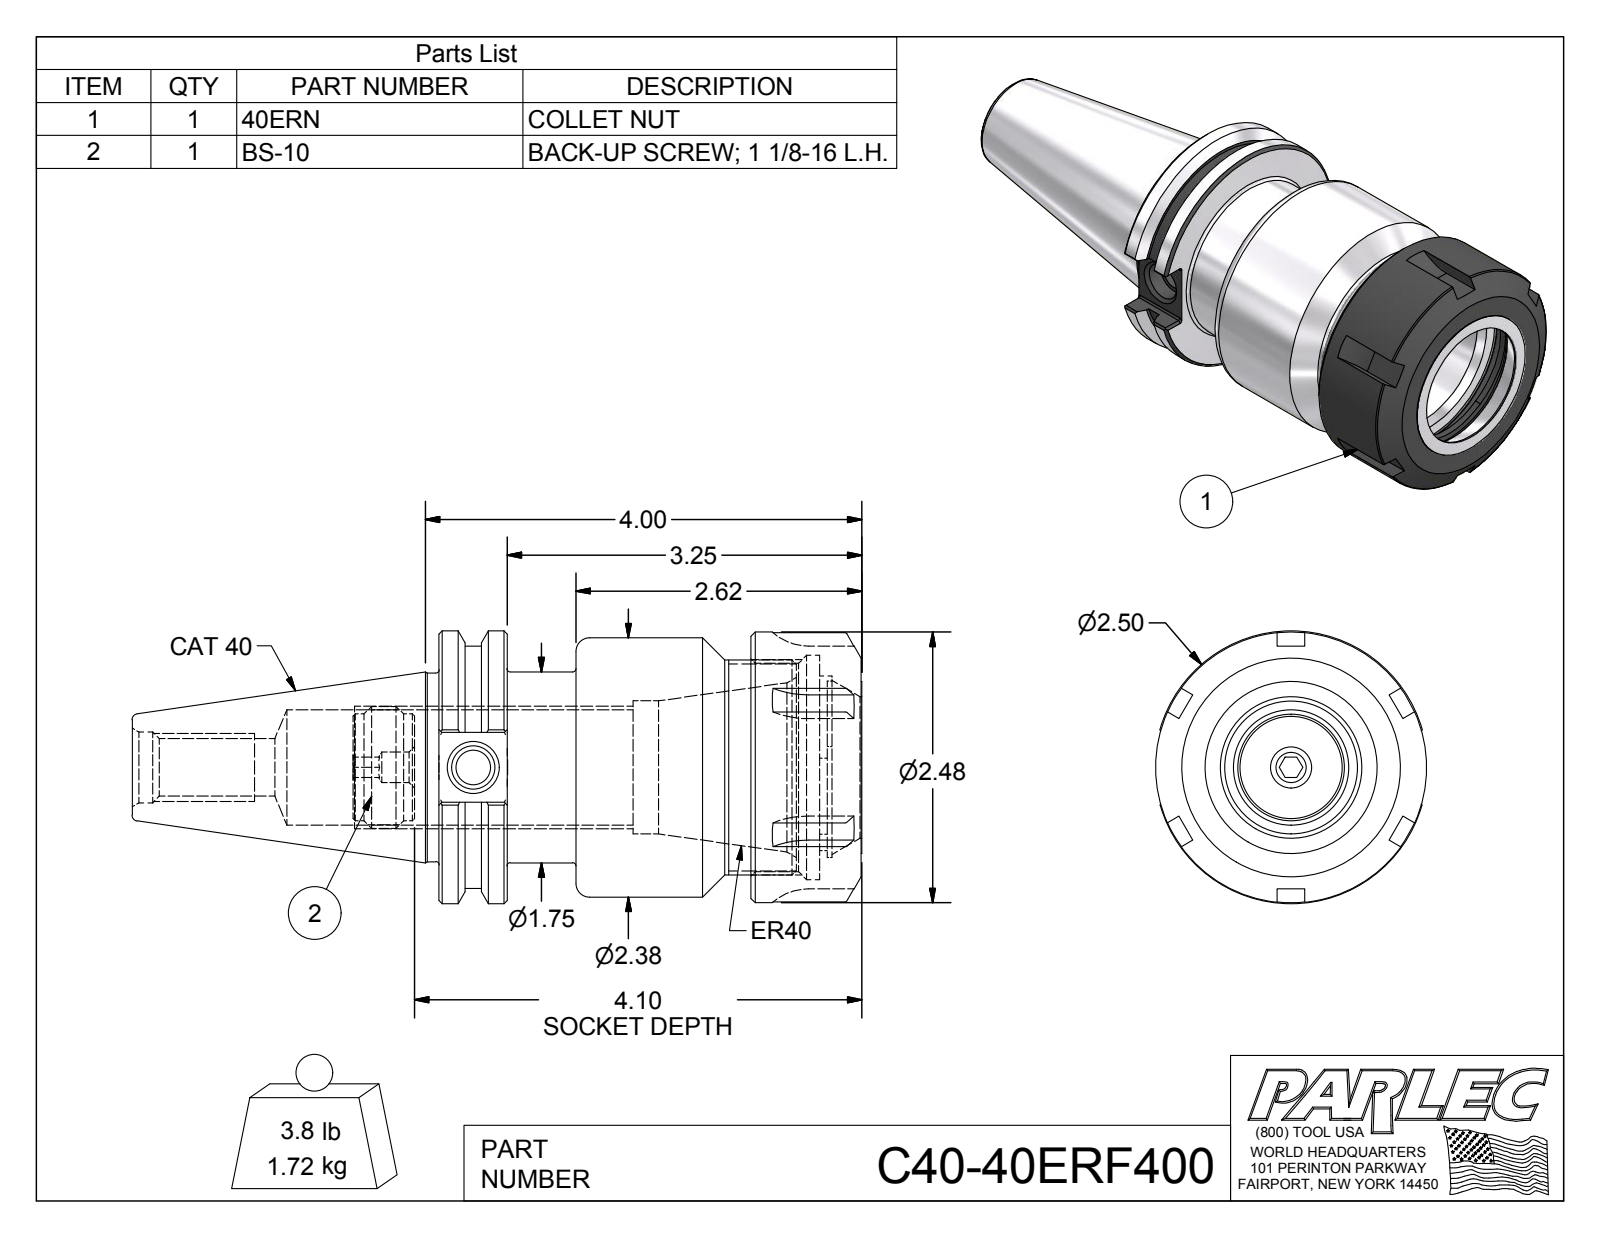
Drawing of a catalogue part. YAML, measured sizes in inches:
part_name: "C40-40ER4-1; 40ERN; BS-10; C40-40ERF400"
step_written_by: "Autodesk Inventor 2016 (AUTOMOTIVE_DESIGN)"
units: inches
bodies: {solids: 3, faces: 188, planar: 76, cylindrical: 52, other: 60}
overall_size: [6.687, 2.5, 2.48]
volume: 13.56
surface_area: 88.6
round_holes:
  - {diameter: 0.22, count: 1}
  - {diameter: 0.28, count: 1}
  - {diameter: 0.315, count: 1}
  - {diameter: 0.399, count: 1}
  - {diameter: 0.527, count: 1}
  - {diameter: 0.648, count: 1}
  - {diameter: 1.057, count: 1}
  - {diameter: 1.22, count: 1}
  - {diameter: 1.3, count: 1}
  - {diameter: 1.618, count: 1}
  - {diameter: 1.909, count: 1}
  - {diameter: 2.057, count: 1}
round_bosses_or_shafts:
  - {diameter: 2.5, count: 1}
  - {diameter: 2.48, count: 1}
  - {diameter: 2.375, count: 1}
  - {diameter: 2.219, count: 1}
  - {diameter: 1.969, count: 1}
  - {diameter: 1.75, count: 1}
  - {diameter: 1.73, count: 1}
  - {diameter: 1.118, count: 1}
partial_cylinders:
  - {radius: 0.02, count: 24}
  - {radius: 0.728, count: 1}
  - {radius: 0.827, count: 1}
face_to_face_distances: [3.875, 0.625, 3.25, 1.025, 2.85, 2.225, 3.485, 2.86, 0.635, 0.39]
hole_center_spacings: [0.09]
